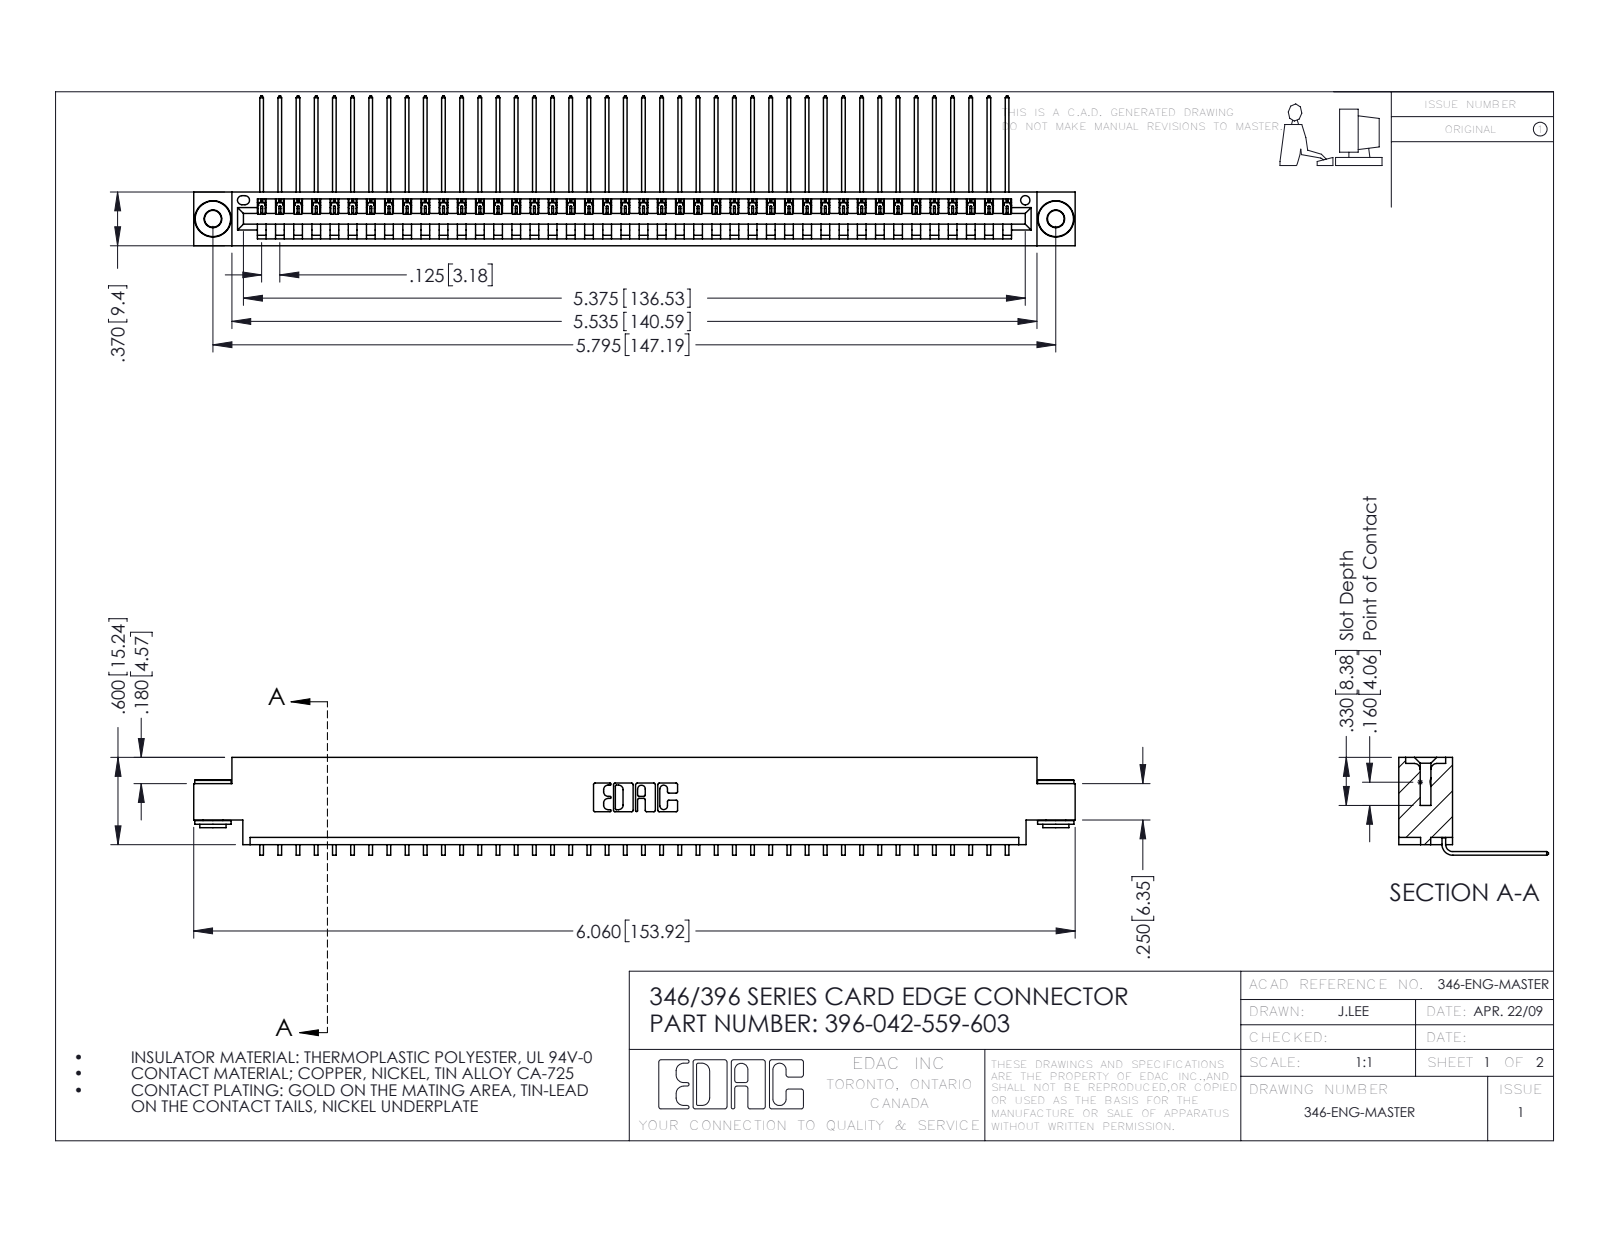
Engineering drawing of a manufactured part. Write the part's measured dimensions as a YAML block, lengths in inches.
part_name: "396-042-559-603; 345-250-002_345-250-002-102; 346 Part_0.170 Offset - 0.156 Dia-TH; 345-292-001_558 559 Tail - 1"
step_written_by: "SolidWorks 2016 (CONFIG_CONTROL_DESIGN)"
units: inches
bodies: {solids: 45, faces: 2684, planar: 1854, cylindrical: 822, other: 8}
overall_size: [6.06, 1.03, 0.673]
volume: 0.899
surface_area: 30.44
round_holes:
  - {diameter: 0.116, count: 2}
  - {diameter: 0.156, count: 2}
  - {diameter: 0.064, count: 1}
round_bosses_or_shafts:
  - {diameter: 0.25, count: 2}
  - {diameter: 0.18, count: 2}
  - {diameter: 0.136, count: 2}
partial_cylinders:
  - {radius: 0.006, count: 84}
  - {radius: 0.01, count: 22}
  - {radius: 0.007, count: 6}
  - {radius: 0.031, count: 6}
  - {radius: 0.026, count: 3}
  - {radius: 0.031, count: 2}
  - {radius: 0.04, count: 2}
  - {radius: 0.014, count: 1}
face_to_face_distances: [0.048, 0.322, 0.37, 0.025, 0.25, 0.072, 0.298, 0.148, 0.222, 0.1]
hole_center_spacings: [0.246, 5.586, 5.795]
